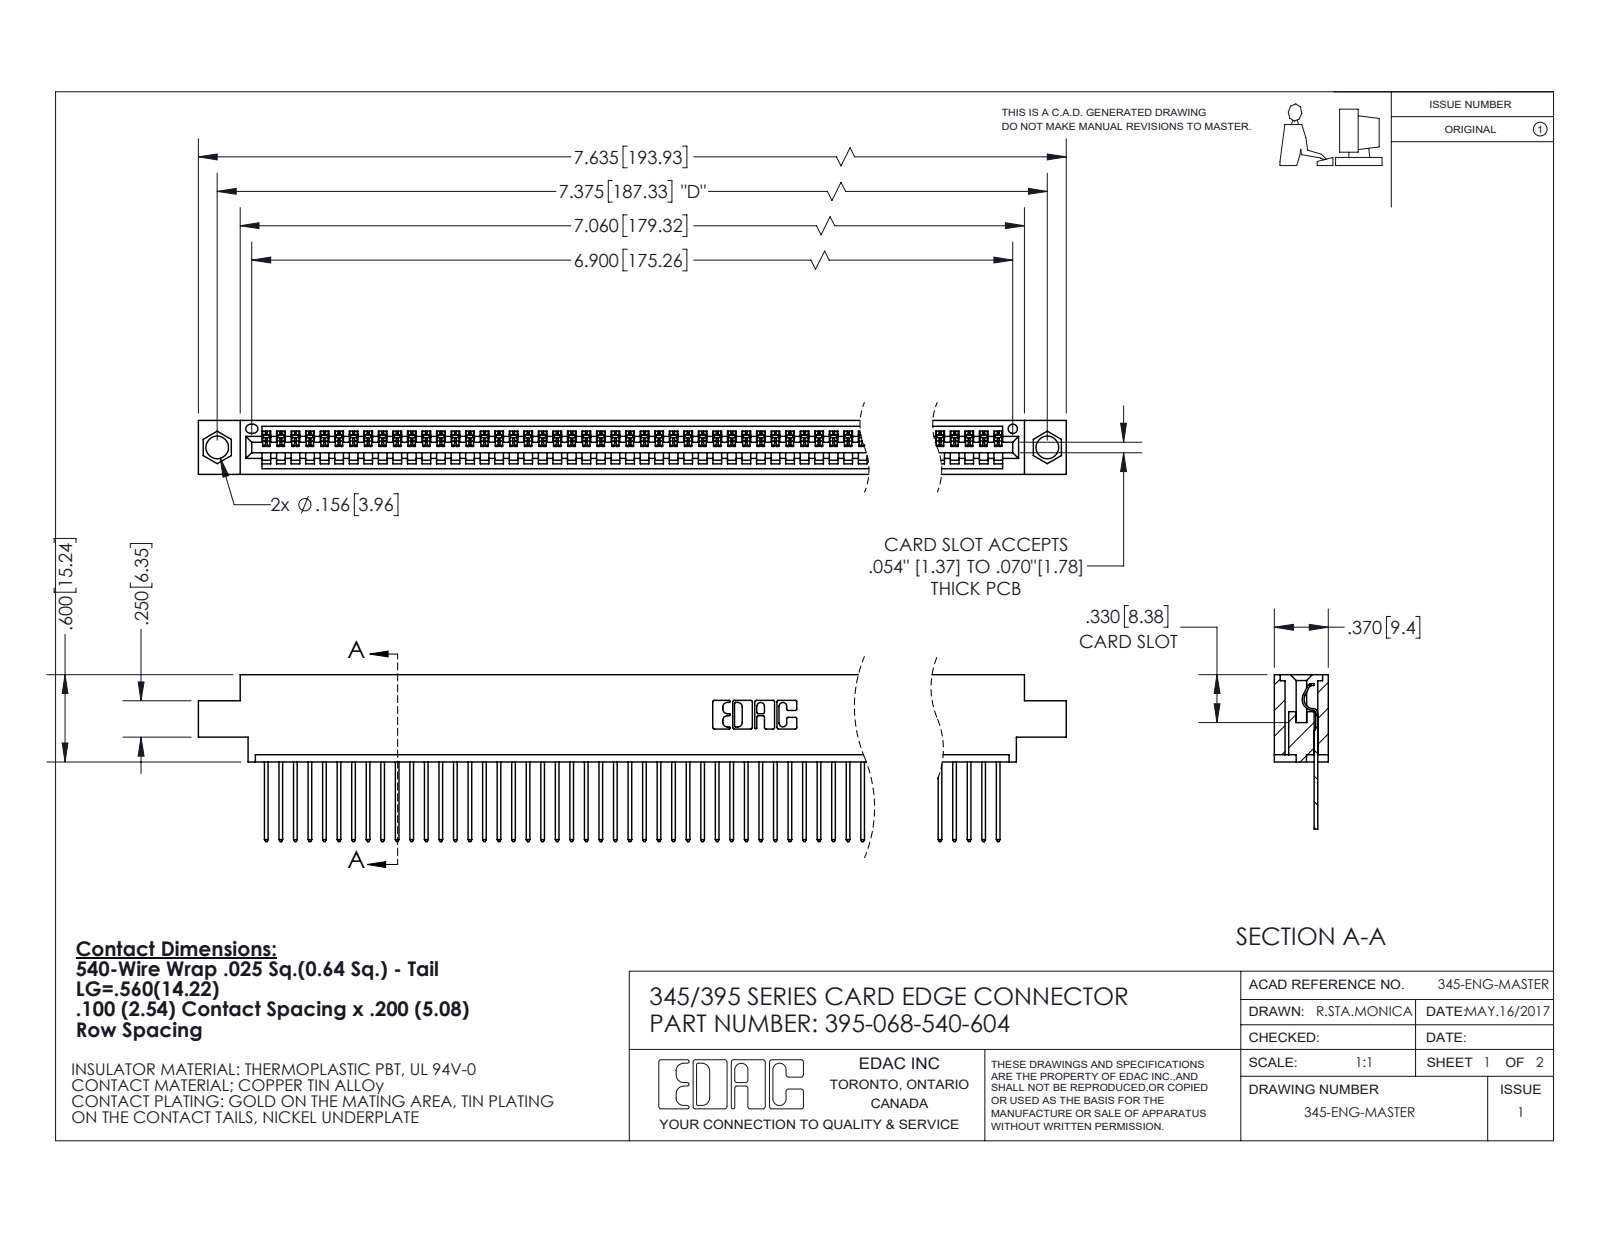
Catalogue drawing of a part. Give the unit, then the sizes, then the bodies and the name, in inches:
Units: inches
Overall size (bounding box): 7.635 × 1.147 × 0.37
Round holes (diameter × count): ⌀0.156 ×2, ⌀0.064 ×1
Partial cylindrical surfaces — rounded edges, fillets, slot ends (radius × count): R0.006 ×136, R0.01 ×136, R0.01 ×22, R0.007 ×6, R0.031 ×6, R0.026 ×3, R0.031 ×2, R0.04 ×2
Main face-to-face distances: 0.072, 0.298, 0.37, 0.098, 0.272, 0.025, 0.2, 0.225, 0.175, 0.149
Hole centre spacings: 0.27, 7.139, 7.375
Volume: 1.129 in³ · Surface area: 39.64 in²
Bodies: 69 solids, 4088 faces (2818 planar, 1270 cylindrical, 0 other)
Part name (STEP PRODUCT): 395-068-540-604; 345 Part_0.170 Offset - 0.156 Dia-TI; 345-292-001_345-293-140
STEP written by: SolidWorks 2020 (CONFIG_CONTROL_DESIGN)
